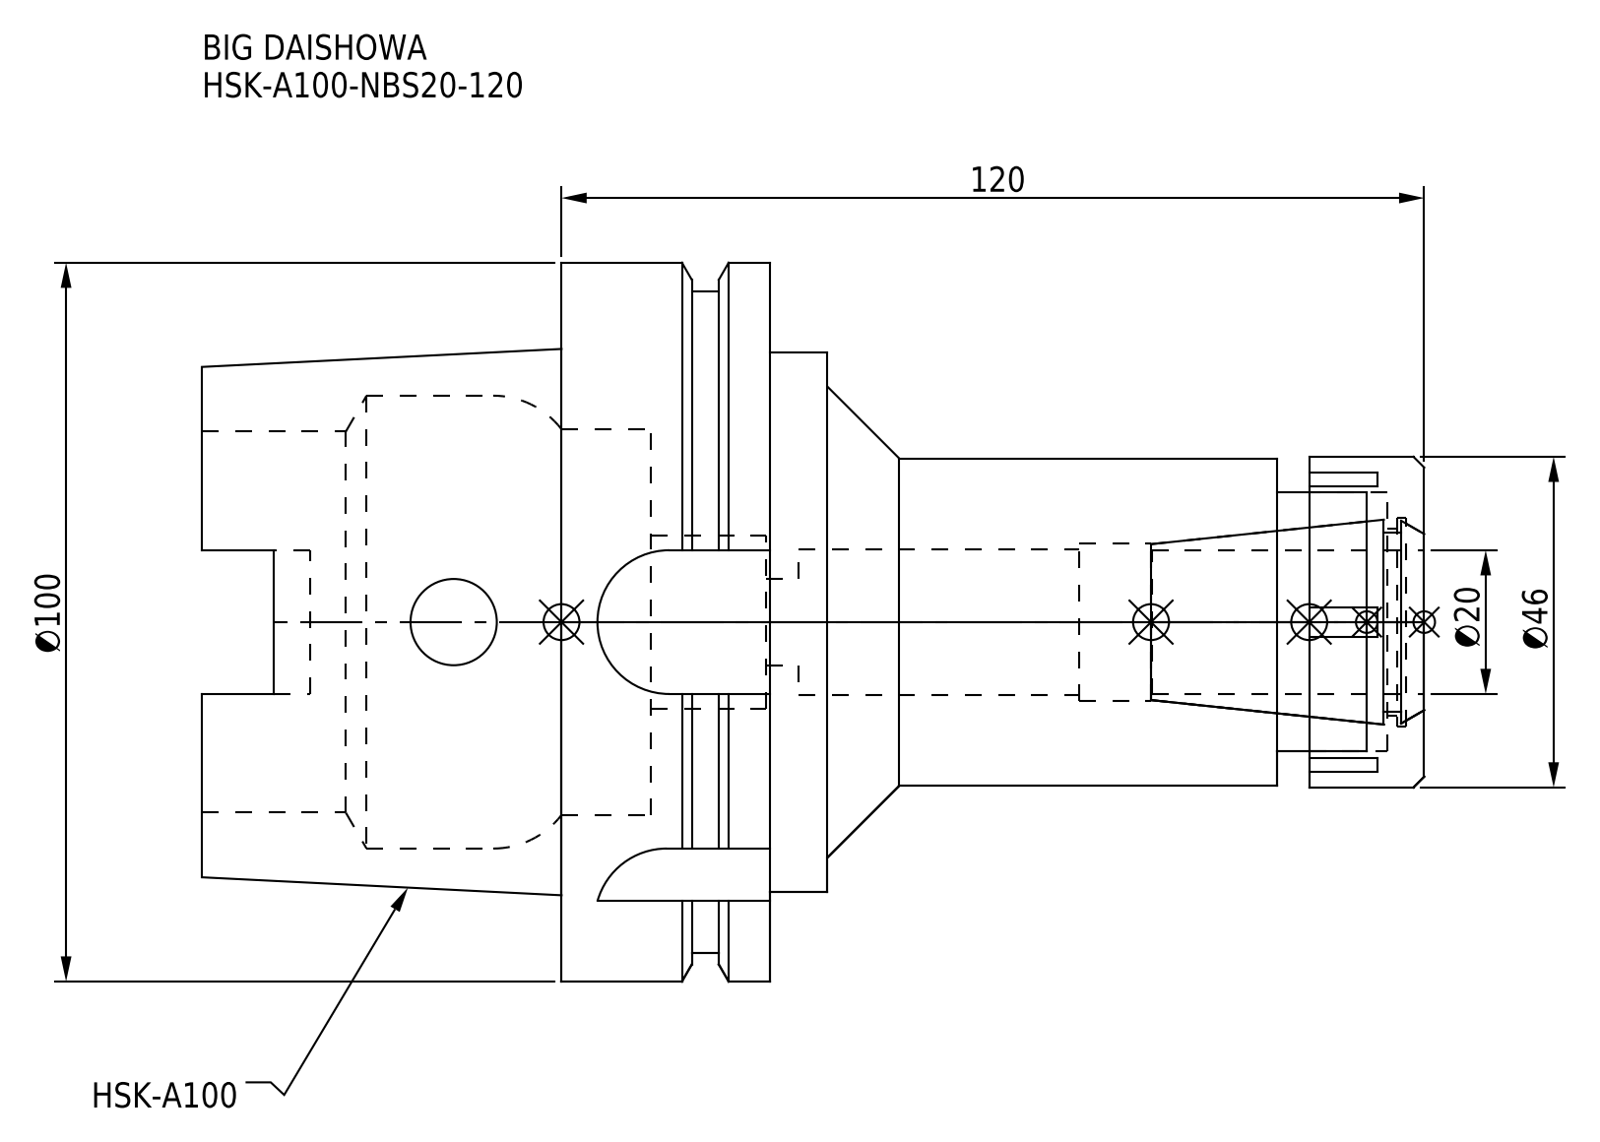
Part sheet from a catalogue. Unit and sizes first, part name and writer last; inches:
Units: inches
Overall size (bounding box): 6.693 × 3.937 × 3.937
Round holes (diameter × count): ⌀0.472 ×2, ⌀0.799 ×1, ⌀0.866 ×1, ⌀0.945 ×1, ⌀1.024 ×1, ⌀1.142 ×1, ⌀1.417 ×1, ⌀2.087 ×1, ⌀2.118 ×1, ⌀2.48 ×1
Round bosses / shafts (diameter × count): ⌀3.937 ×1, ⌀3.622 ×1, ⌀2.953 ×1, ⌀1.811 ×1, ⌀1.791 ×1
Partial cylindrical surfaces — rounded edges, fillets, slot ends (radius × count): R0.192 ×4, R0.394 ×4
Main face-to-face distances: 1.142, 0.315, 0.652, 0.49, 3.268, 3.425, 3.11, 0.967, 1.457, 2.459
Volume: 23.91 in³ · Surface area: 113.9 in²
Bodies: 2 solids, 138 faces (66 planar, 50 cylindrical, 22 other)
Part name (STEP PRODUCT): HSK-A100-NBS20-120; NBN20_1.stp; DXF_TEMP_ASSY_ASM_4_ASM.stp; HSK-A100-NBS20-120.stp (+3 more)
STEP written by: SolidWorks 2019 (CONFIG_CONTROL_DESIGN)
